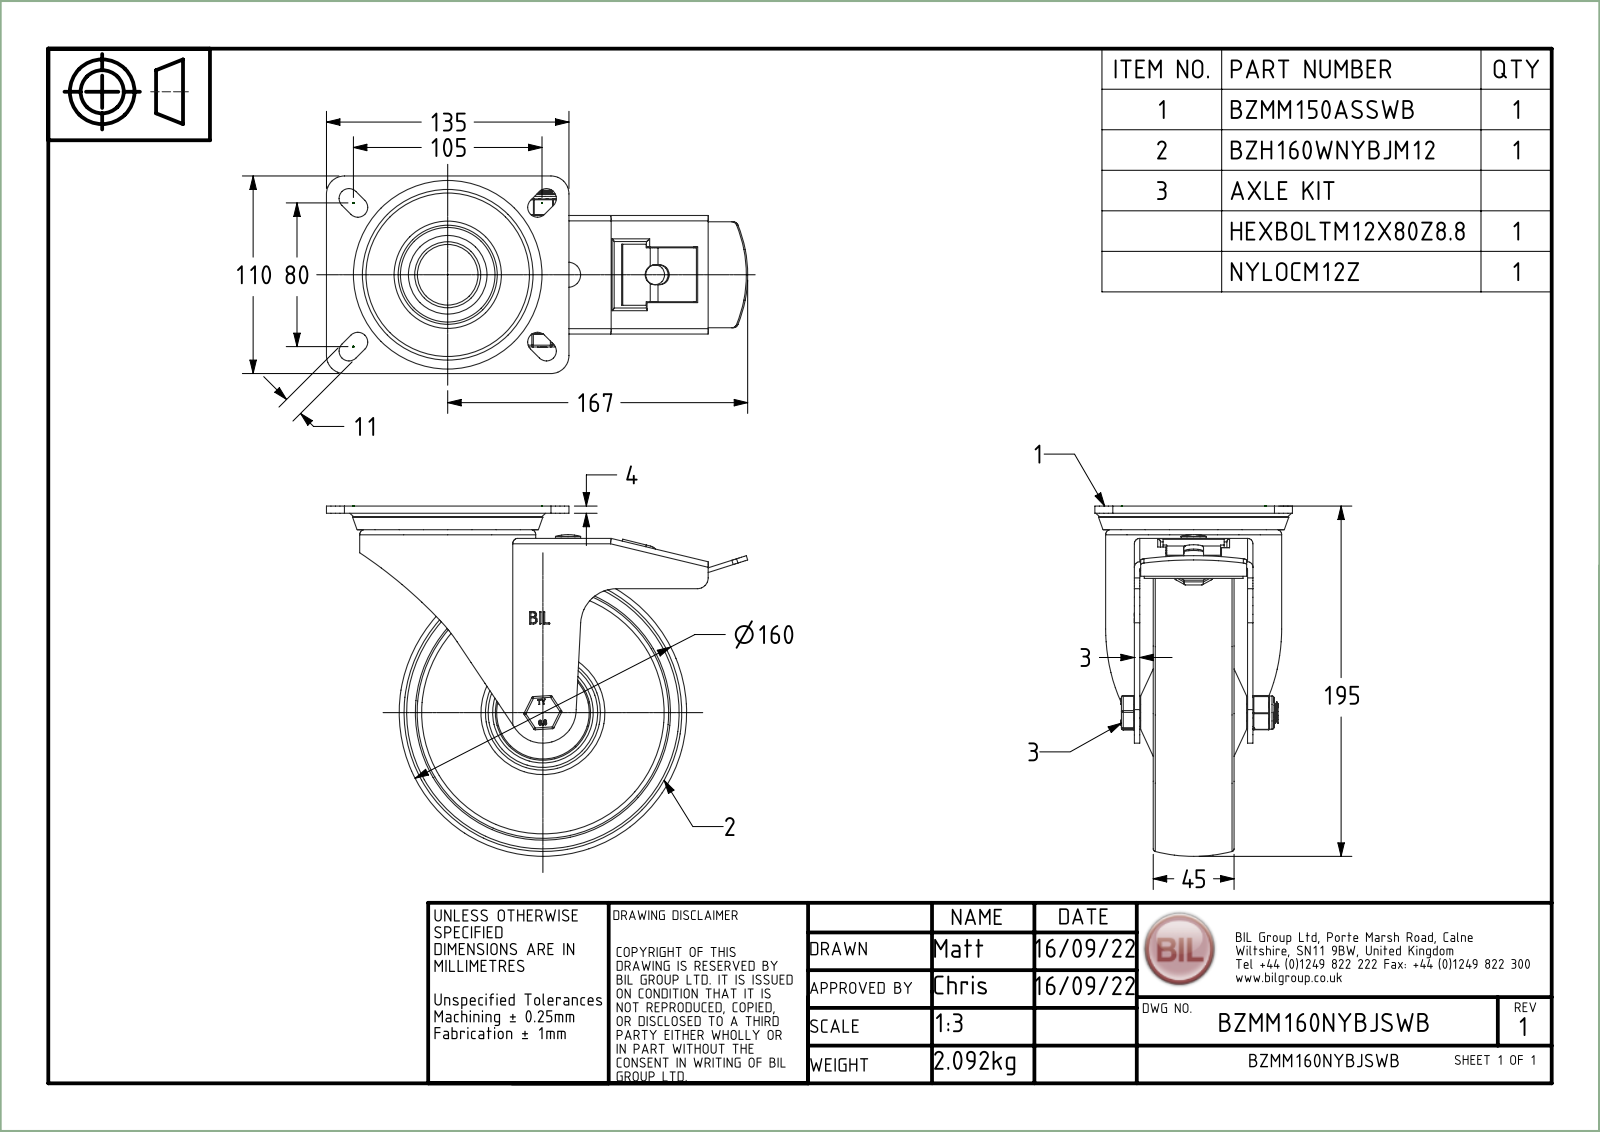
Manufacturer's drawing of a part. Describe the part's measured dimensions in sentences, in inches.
The part is named "ZINC PLATED, PRESSED STEEL TOP PLATE; ZINC PLATED, PRESSED STEEL TOP PLATE Geometry; BALL BEARINGS; BZMM150ASSWB (+7 more)". Its 3-D file was written by "Spatial InterOp 3D (AUTOMOTIVE_DESIGN)". It is 67 solids with 1248 faces: 396 planar, 383 cylindrical and 469 other. Overall it measures 9.232 by 7.677 by 4.331 inches. Its volume is 33.85 cubic inches and its surface area 422.2 square inches. Round holes: 1 of diameter 0.315, 1 of diameter 0.433, 1 of diameter 0.472, 1 of diameter 0.48, 1 of diameter 0.488, 1 of diameter 0.551, 1 of diameter 1.122, 1 of diameter 1.213, 1 of diameter 1.329, 1 of diameter 1.398, 1 of diameter 1.565, 1 of diameter 1.587. Round bosses or shafts: 1 of diameter 3.858, 1 of diameter 3.071, 1 of diameter 2.52, 1 of diameter 2.087, 1 of diameter 1.969, 1 of diameter 1.89, 1 of diameter 1.606, 1 of diameter 1.232. Partial cylindrical surfaces (rounded edges, fillets, slot ends): 18 of radius 0.02, 12 of radius 0.039, 10 of radius 0.059, 10 of radius 0.217, 6 of radius 0.01, 6 of radius 0.098, 6 of radius 0.118, 4 of radius 0.394. The main face-to-face distances are 0.118, 0.354, 0.197, 0.157, 1.24, 2.48, 0.472, 0.128, 0.63, 0.827. The hole center spacings are 2.638.
